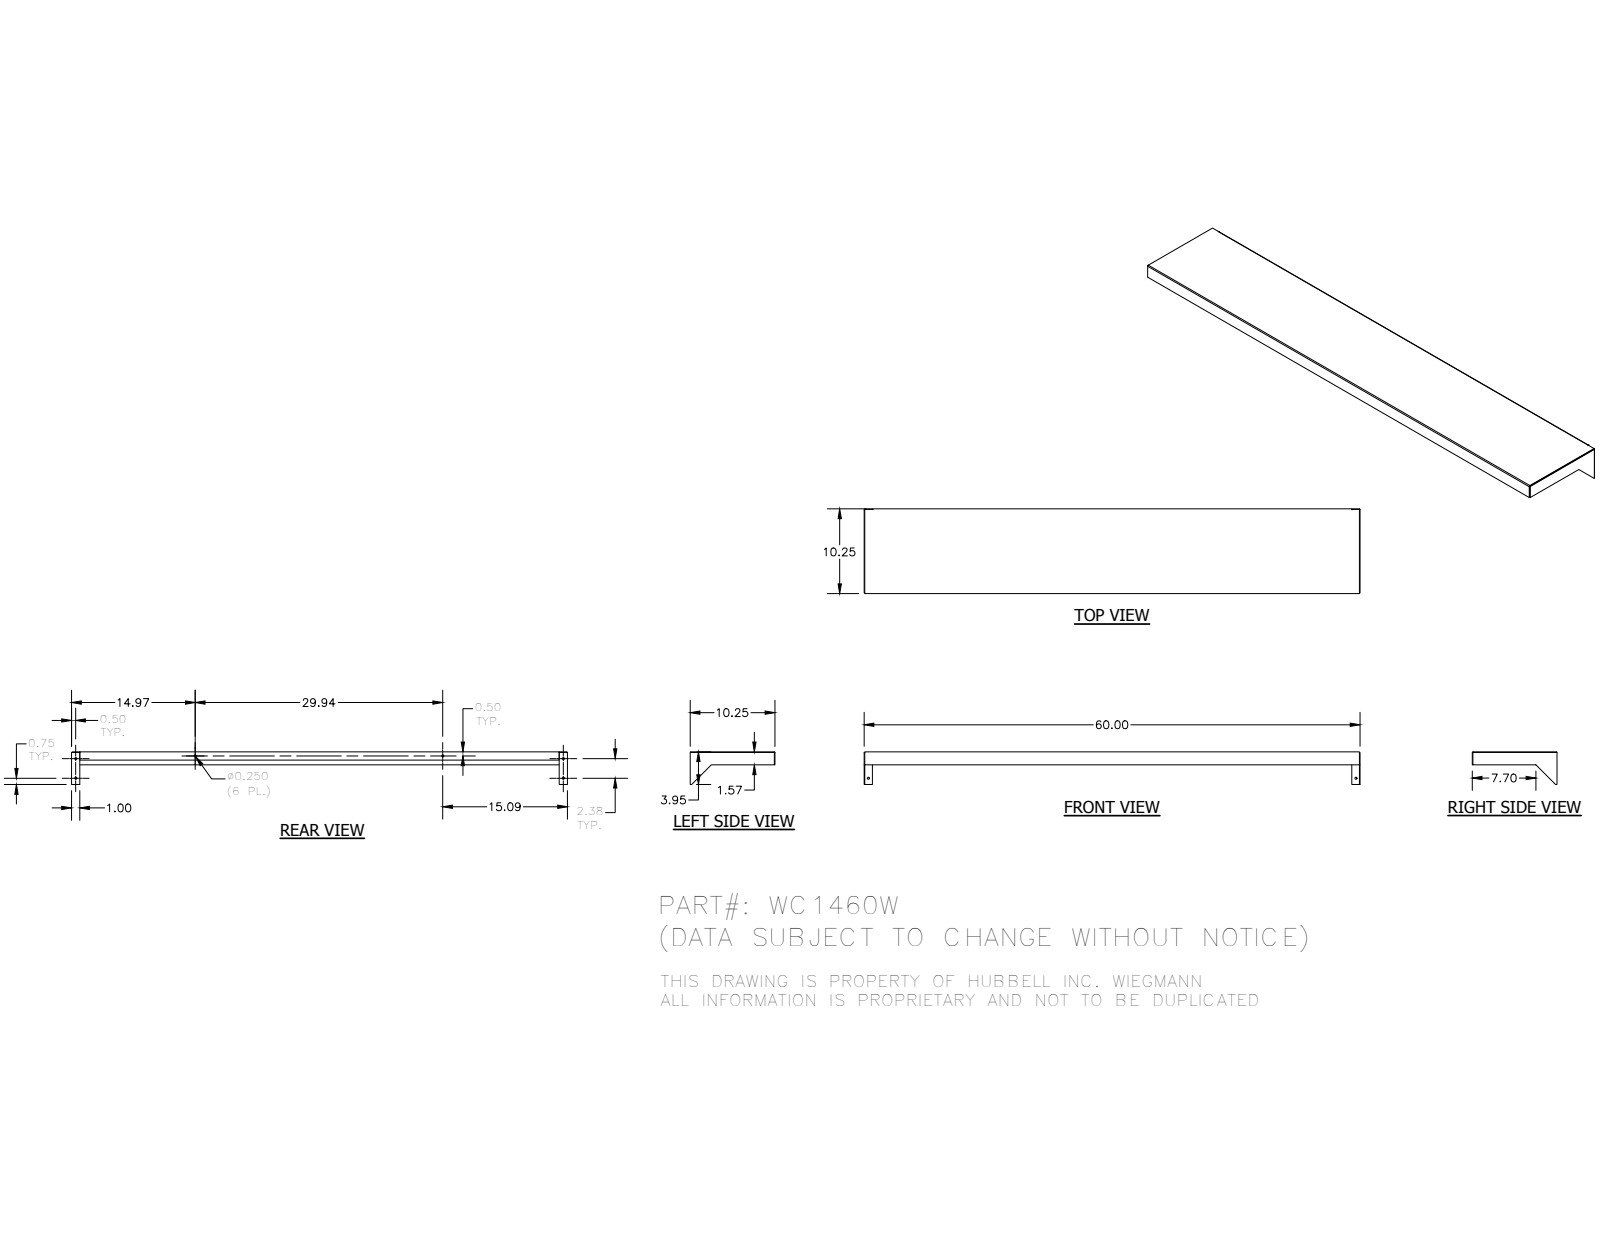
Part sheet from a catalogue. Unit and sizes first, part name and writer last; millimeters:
Units: millimetres
Overall size (bounding box): 1524 × 260.35 × 100.31
Round holes (diameter × count): ⌀6.35 ×6
Partial cylindrical surfaces — rounded edges, fillets, slot ends (radius × count): R0.79 ×4, R2.67 ×4
Main face-to-face distances: 1.88, 258.47, 256.59, 260.35, 1522.12, 1520.24, 1524, 39.98, 38.1, 25.4
Hole centre spacings: 60.33, 1498.6, 1499.81, 367.6, 370.76, 373.85, 376.96, 760.42
Volume: 966 524 mm³ · Surface area: 1 038 000 mm²
Bodies: 3 solids, 68 faces (54 planar, 14 cylindrical, 0 other)
Part name (STEP PRODUCT): WC1460WBKP; WC14WRS; WC14WLS; WC14W
STEP written by: Autodesk Inventor 2016 (AUTOMOTIVE_DESIGN)
